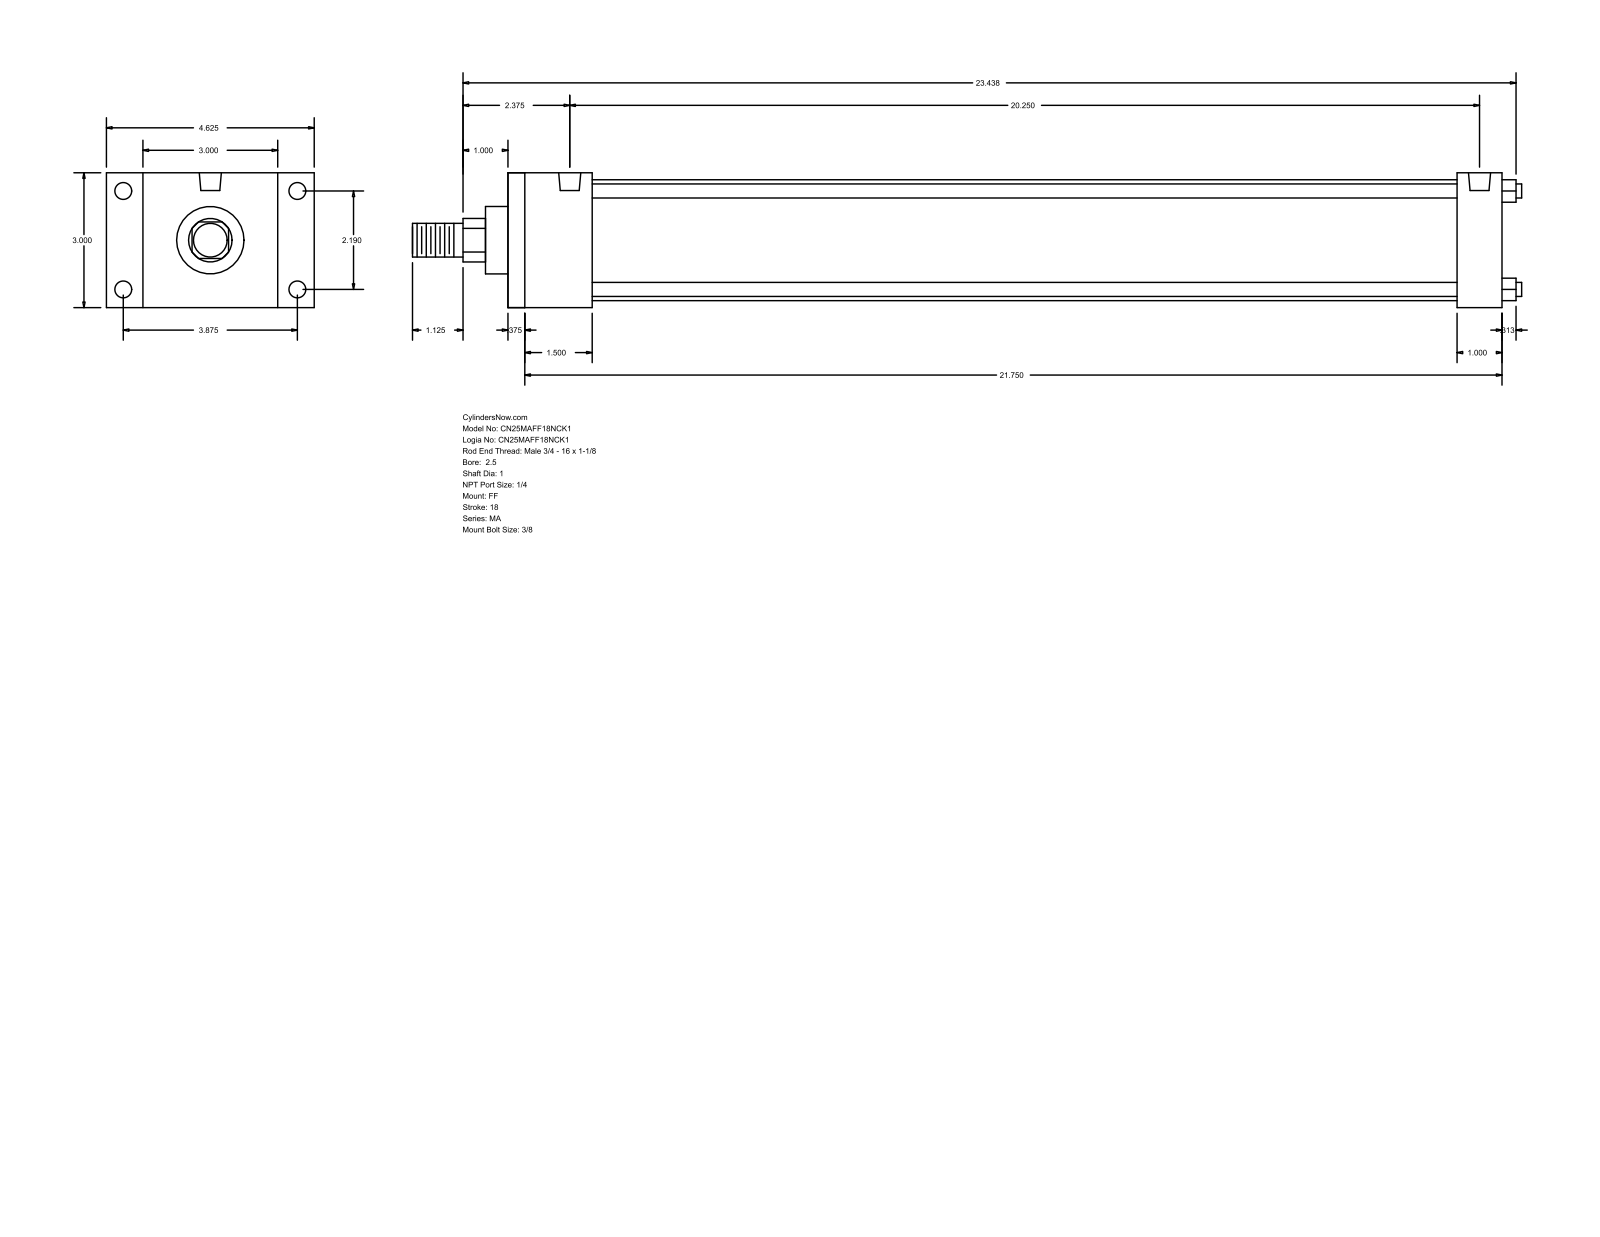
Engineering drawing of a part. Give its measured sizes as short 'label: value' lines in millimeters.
name: MA_FF__0250_1
written by: GSSL Pune (CONFIG_CONTROL_DESIGN)
unit: mm
bodies: 0 solids, 92 faces (64 planar, 28 cylindrical, 0 other)
size: 627.06 × 117.47 × 76.2
holes: 4× ⌀7.94, 4× ⌀9.53, 2× ⌀12.49
bosses: 4× ⌀7.94, 1× ⌀68.33, 1× ⌀38.1, 1× ⌀25.4, 1× ⌀19.05
rounds: 1× R12.29
face distances: 76.2, 561.98, 9.52, 552.46, 25.4, 47.63, 536.58, 38.11, 527.06, 488.95
hole spacings: 55.62, 98.42, 113.05, 514.34
